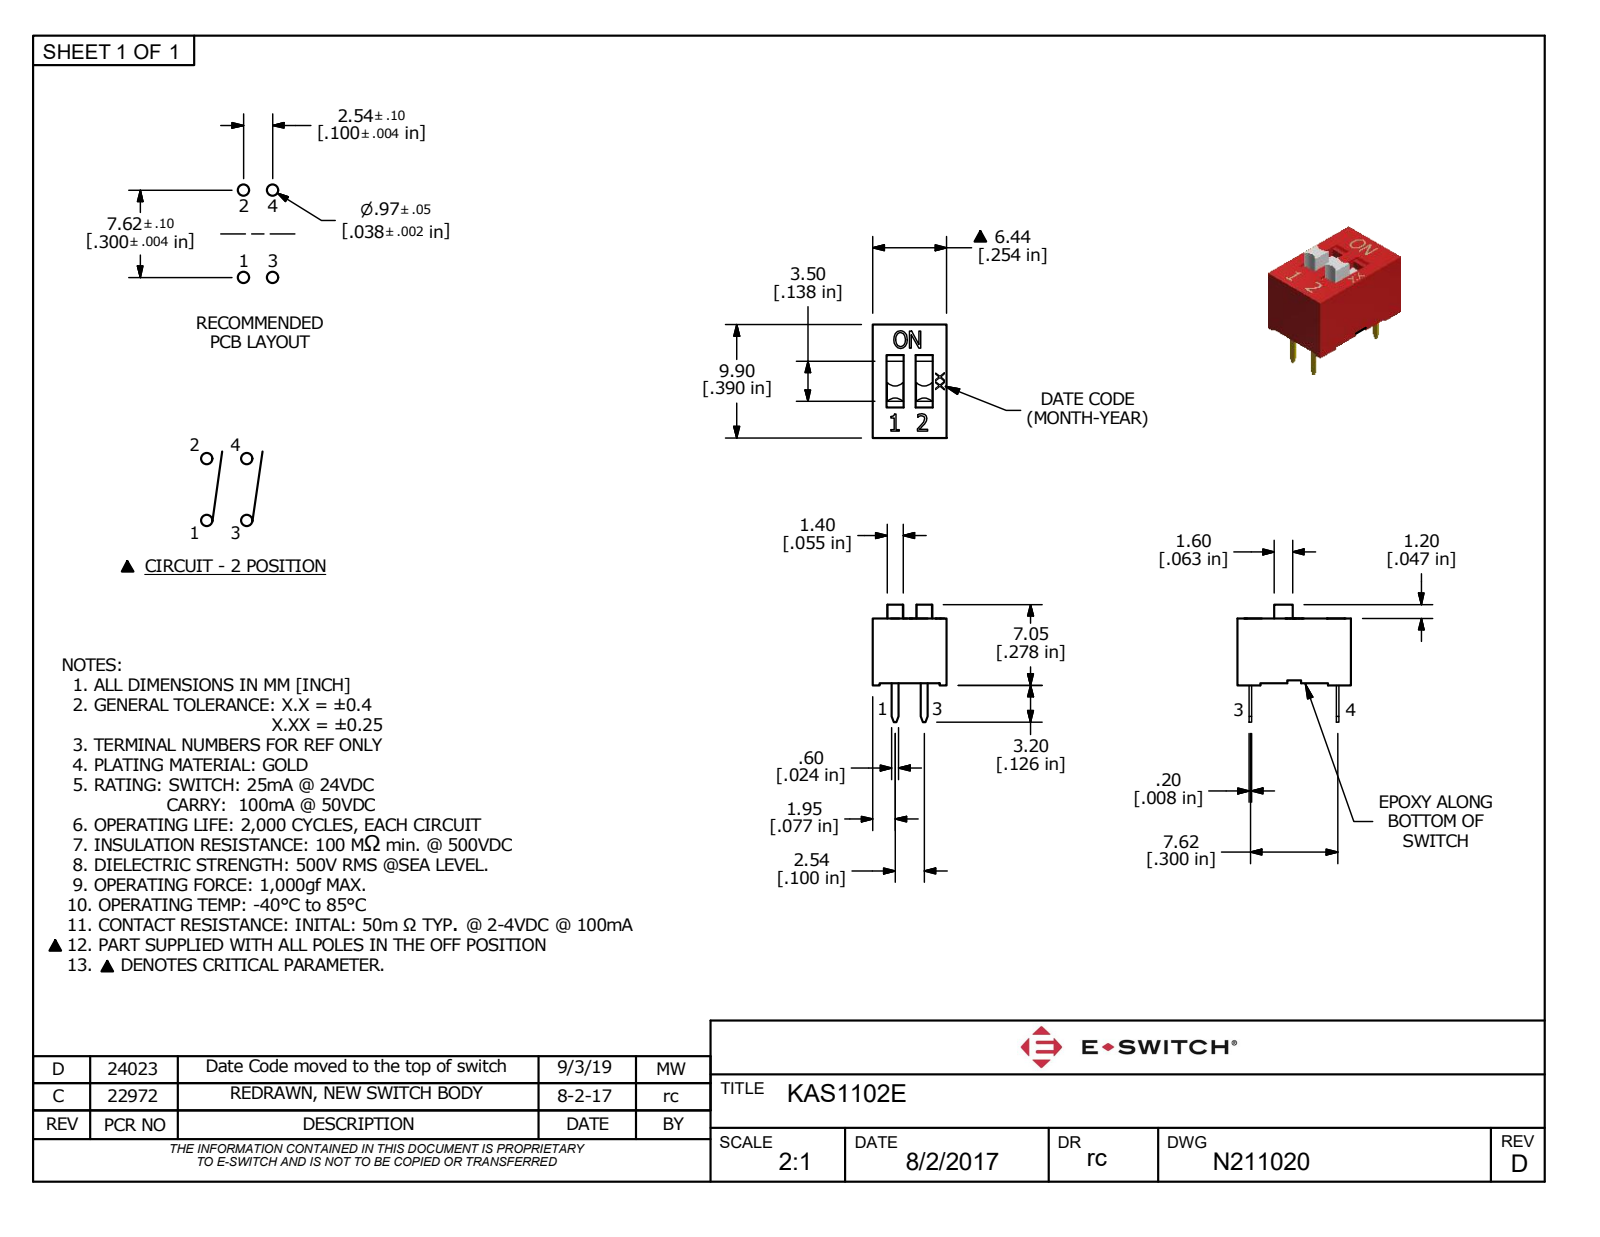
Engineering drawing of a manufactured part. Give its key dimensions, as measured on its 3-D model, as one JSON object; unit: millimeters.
{"part_name": "N211020; KAS 2 Extended Actuator; KAS TERM 1", "step_written_by": "Autodesk Inventor 2018 (AP242_MANAGED_MODEL_BASED_3D_ENGINEERING_MIM_LF)", "units": "millimeters", "bodies": {"solids": 5, "faces": 182, "planar": 153, "cylindrical": 4, "other": 25}, "overall_size": [10.25, 9.9, 6.44], "volume_mm3": 347, "surface_area_mm2": 407, "partial_cylinders_radius": [[0.9, 4]], "face_to_face_distances": [6.44, 5.34, 9.9, 0.6, 2.54, 1.45, 0.31, 5.65, 1.2, 5.84]}
